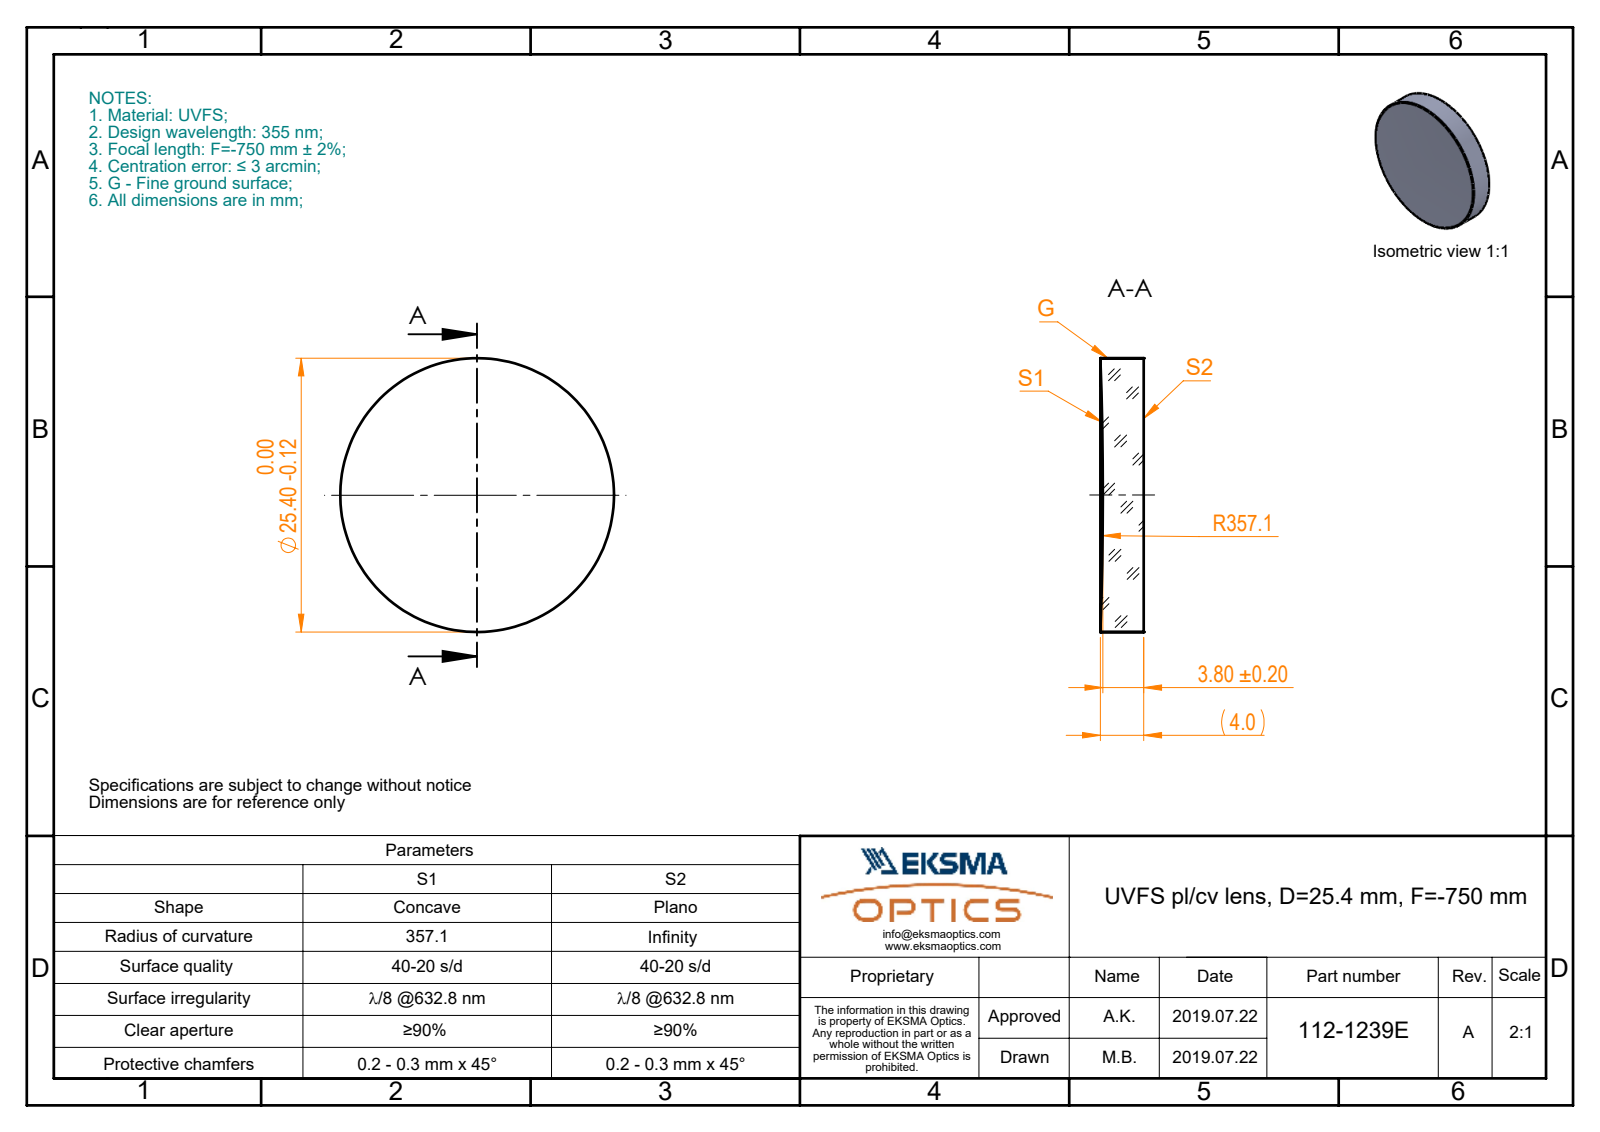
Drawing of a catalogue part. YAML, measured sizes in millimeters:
part_name: "112-1239E UVFS pl-cv 25.4 F-750"
step_written_by: "SolidWorks 2017 (CONFIG_CONTROL_DESIGN)"
units: millimeters
bodies: {solids: 1, faces: 5, planar: 1, cylindrical: 2, other: 2}
overall_size: [25.4, 25.4, 4.03]
volume: 1983
surface_area: 1335
round_bosses_or_shafts:
  - {diameter: 25.4, count: 1}
